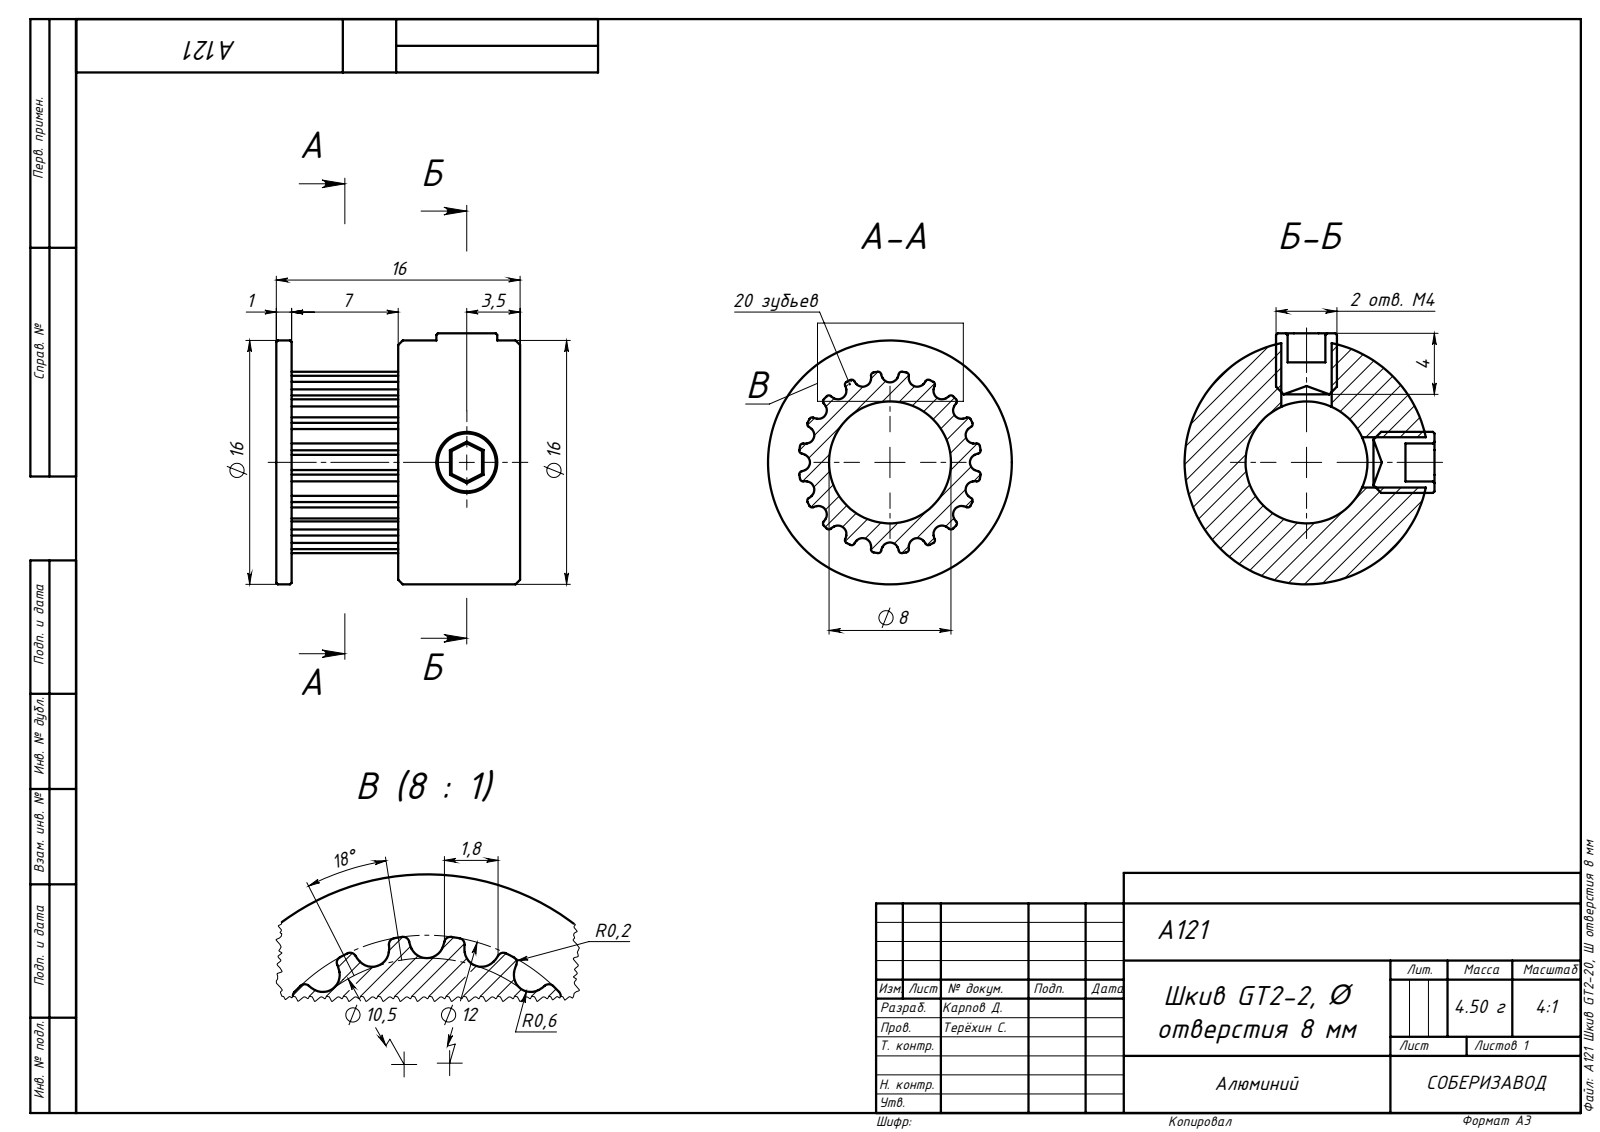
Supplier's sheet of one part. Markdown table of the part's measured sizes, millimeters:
| quantity | value |
| --- | --- |
| part name | A121 Шкив GT2-20, O отверстия 8 мм |
| STEP written by | SolidWorks 2019 (AUTOMOTIVE_DESIGN) |
| units | millimeters |
| bodies | 3 solids, 209 faces (32 planar, 153 cylindrical, 24 other) |
| overall size | 16.46 × 16.4 × 16 |
| volume | 1 699 mm³ |
| surface area | 1 913 mm² |
| round holes (diameter × count) | 3.3 × 2, 8 × 1 |
| round bosses / shafts (diameter × count) | 4 × 2, 16 × 1 |
| partial cylindrical surfaces (radius × count) | 0.2 × 40, 1 × 40, 0.56 × 20, 6 × 1 |
| main face-to-face distances | 8, 16, 1, 15, 7, 1.9, 2, 2.24, 2.23 |
